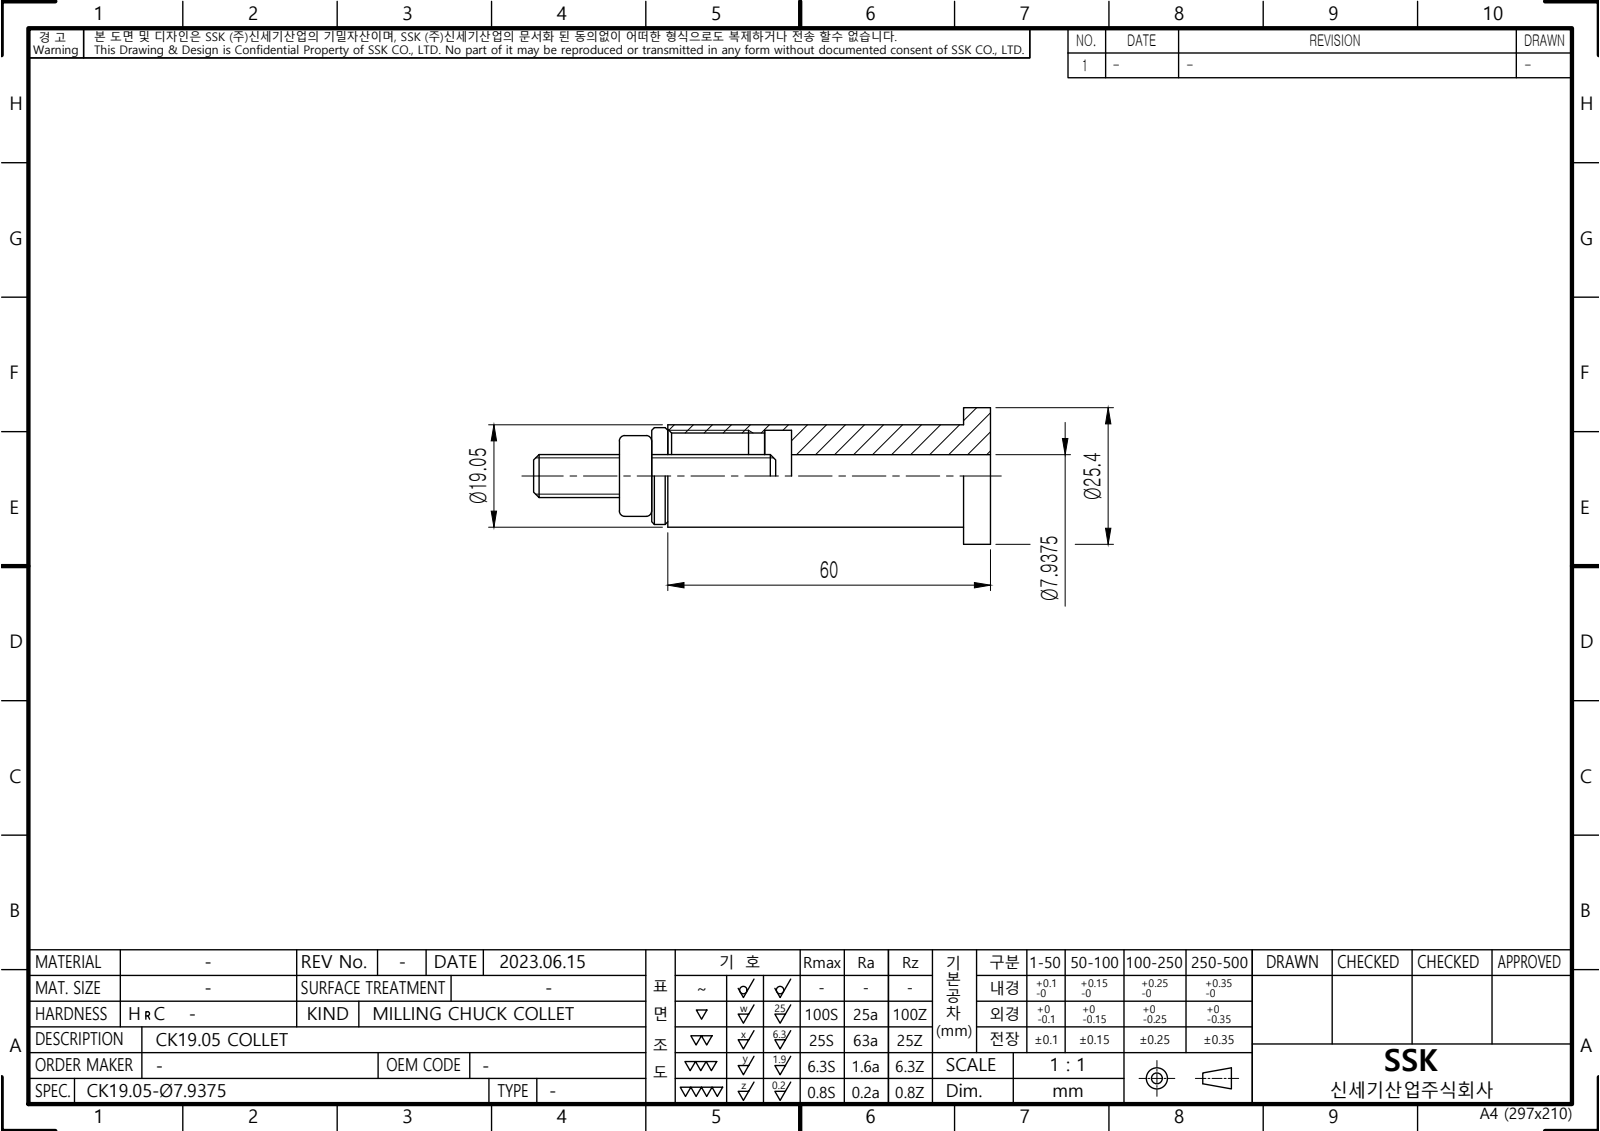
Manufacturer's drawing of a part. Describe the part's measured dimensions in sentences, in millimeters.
The part is named "LO-CK19.05-7.9375". Its 3-D file was written by "Autodesk Inventor 2022 (AUTOMOTIVE_DESIGN)". It is 1 solid with 10 faces: 5 planar, 5 cylindrical and 0 other. Overall it measures 60 by 25.4 by 25.4 millimeters. Its volume is 11 662 cubic millimeters and its surface area 6 751 square millimeters. Round holes: 1 of diameter 7.94, 1 of diameter 15.92, 1 of diameter 17. Round bosses or shafts: 1 of diameter 25.4, 1 of diameter 19.05. The main face-to-face distances are 5, 37, 32, 23, 55, 60, 18, 42.
